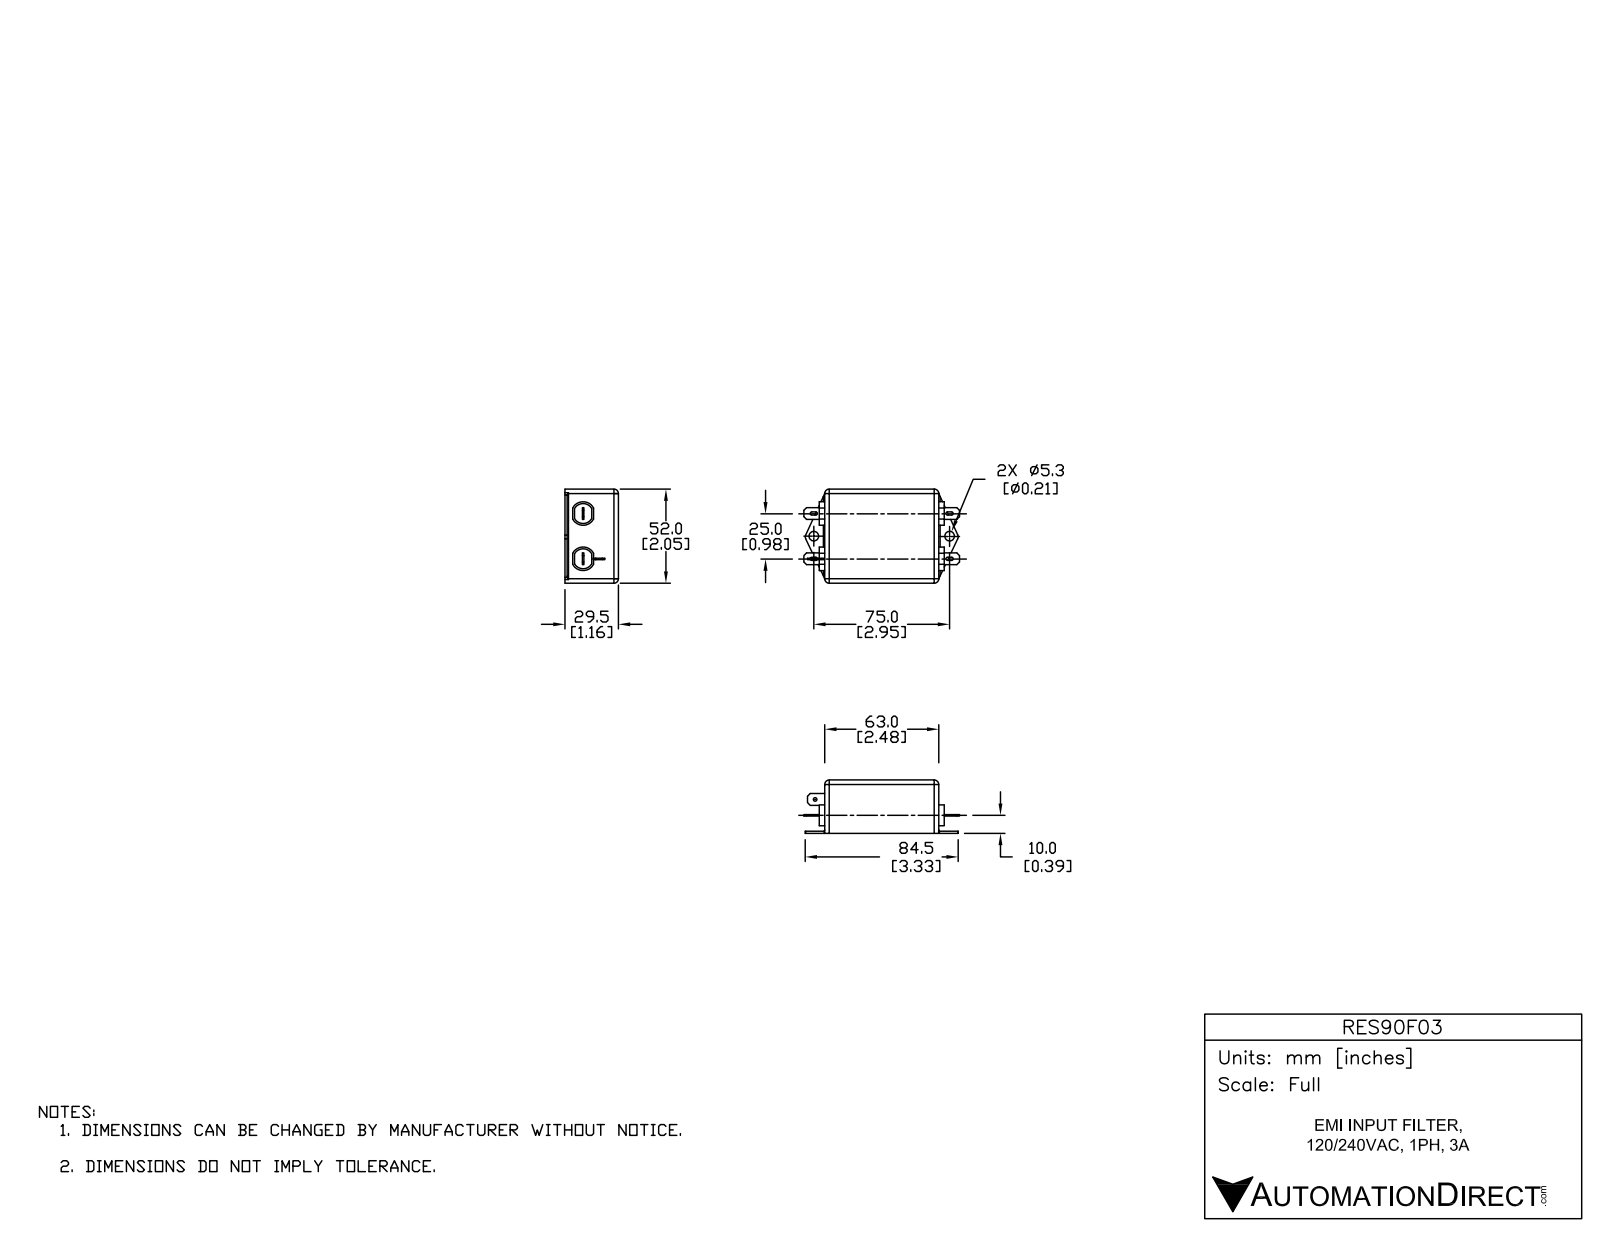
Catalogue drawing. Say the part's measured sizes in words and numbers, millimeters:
The part is named "RES90F03". Its 3-D file was written by "SolidWorks 2015 (AUTOMOTIVE_DESIGN)". It is 1 solid with 133 faces: 79 planar, 50 cylindrical and 4 other. Overall it measures 86 by 52.5 by 29.5 millimeters. Its volume is 98 907 cubic millimeters and its surface area 15 385 square millimeters. Round holes: 2 of diameter 5.3, 1 of diameter 2. Partial cylindrical surfaces (rounded edges, fillets, slot ends): 10 of radius 2.5, 8 of radius 0.88, 2 of radius 0.75, 2 of radius 5.5, 2 of radius 6.5. The main face-to-face distances are 29.5, 52.5, 63, 1.5, 1.2, 28.3, 64.5, 66, 0.8, 10.4. The hole center spacings are 75.
